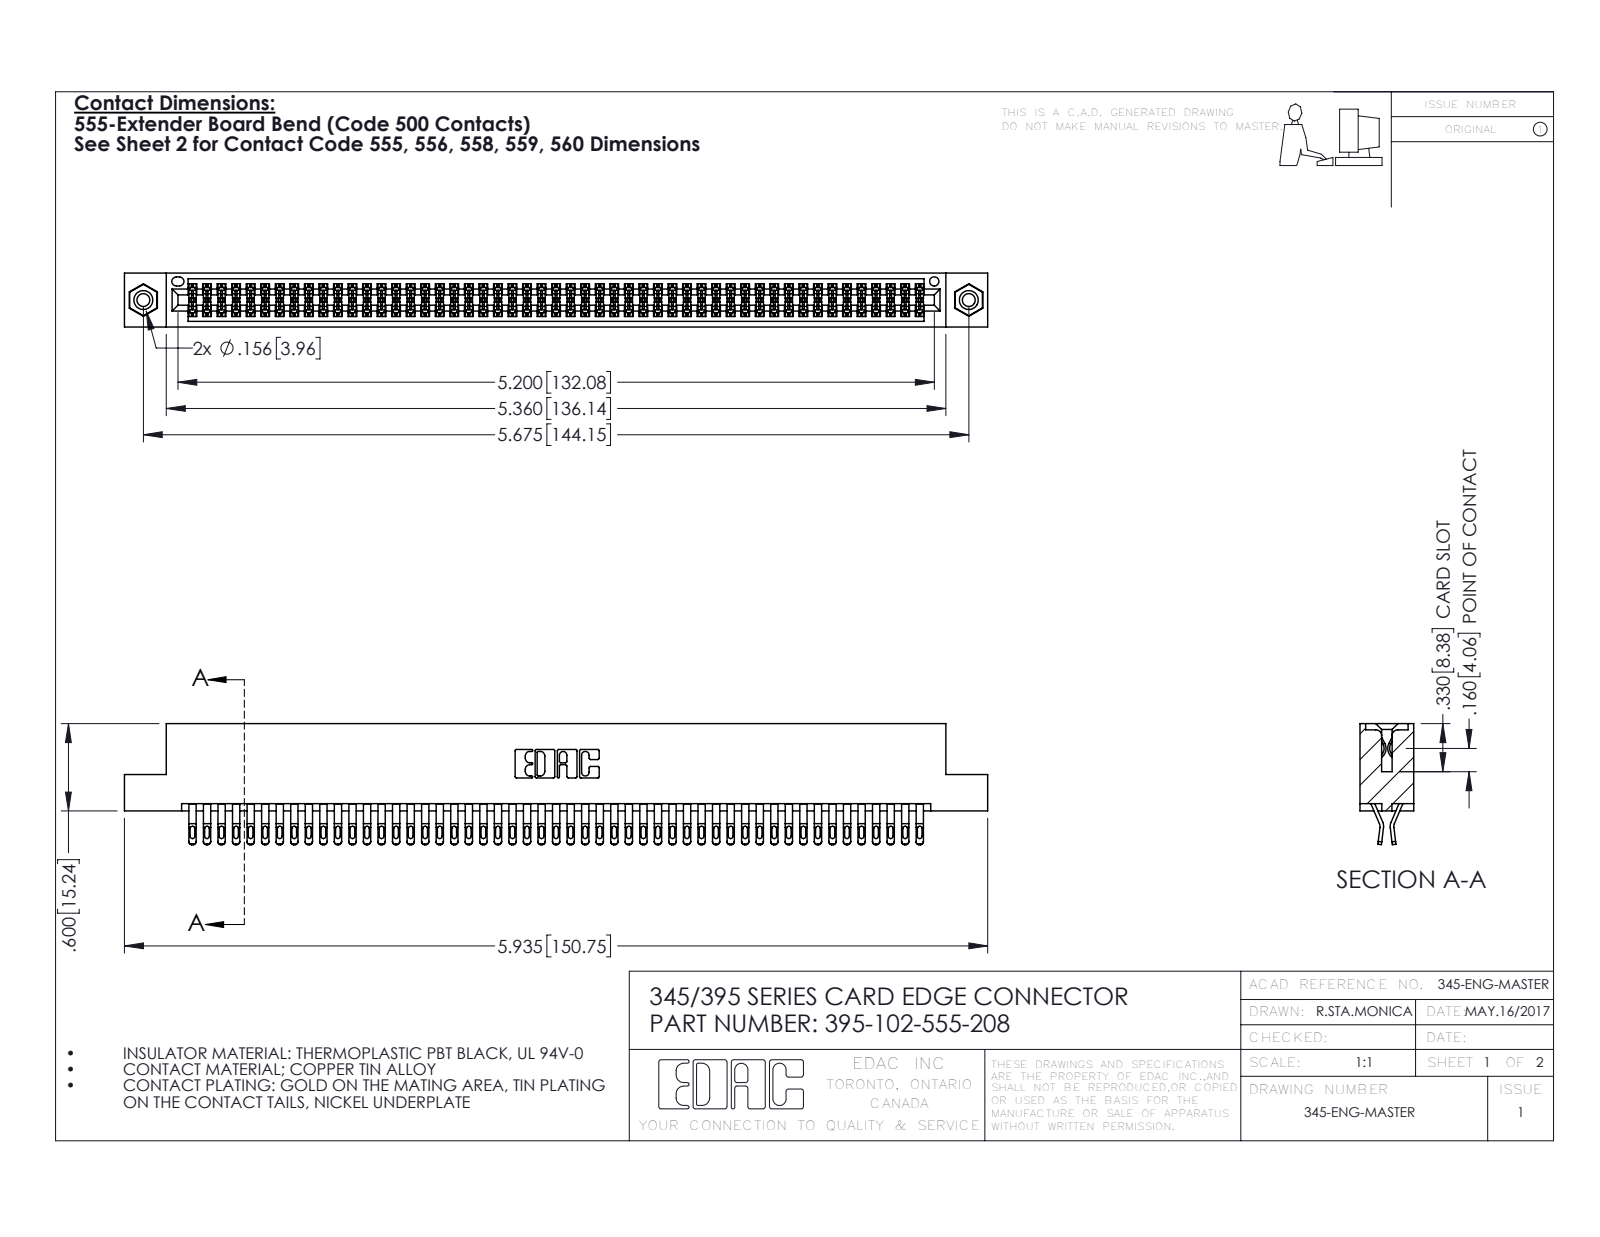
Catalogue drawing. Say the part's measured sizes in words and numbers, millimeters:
The part is named "395-102-555-208; 345-292-001_555 Tail; 345 Part_Flush Mounting Lugs - 0.156 Dia-TI; 345-250-001_345-250-003-102". Its 3-D file was written by "SolidWorks 2016 (CONFIG_CONTROL_DESIGN)". It is 105 solids with 5898 faces: 3274 planar, 2608 cylindrical and 16 other. Overall it measures 150.7 by 21.1 by 9.4 millimeters. Its volume is 15 000 cubic millimeters and its surface area 23 410 square millimeters. Round holes: 2 of diameter 2.3, 2 of diameter 3.2, 2 of diameter 4, 1 of diameter 1.6. Round bosses or shafts: 2 of diameter 3.9. Partial cylindrical surfaces (rounded edges, fillets, slot ends): 255 of radius 0.4, 204 of radius 0.5, 153 of radius 0.2, 22 of radius 0.3, 6 of radius 0.2, 6 of radius 0.8, 3 of radius 0.7, 2 of radius 0.3. The main face-to-face distances are 1.8, 7.6, 0.6, 9.4, 5.1, 2.5, 6.9, 5.7, 4.4, 3.8. The hole center spacings are 6.9, 138.2, 144.1.
